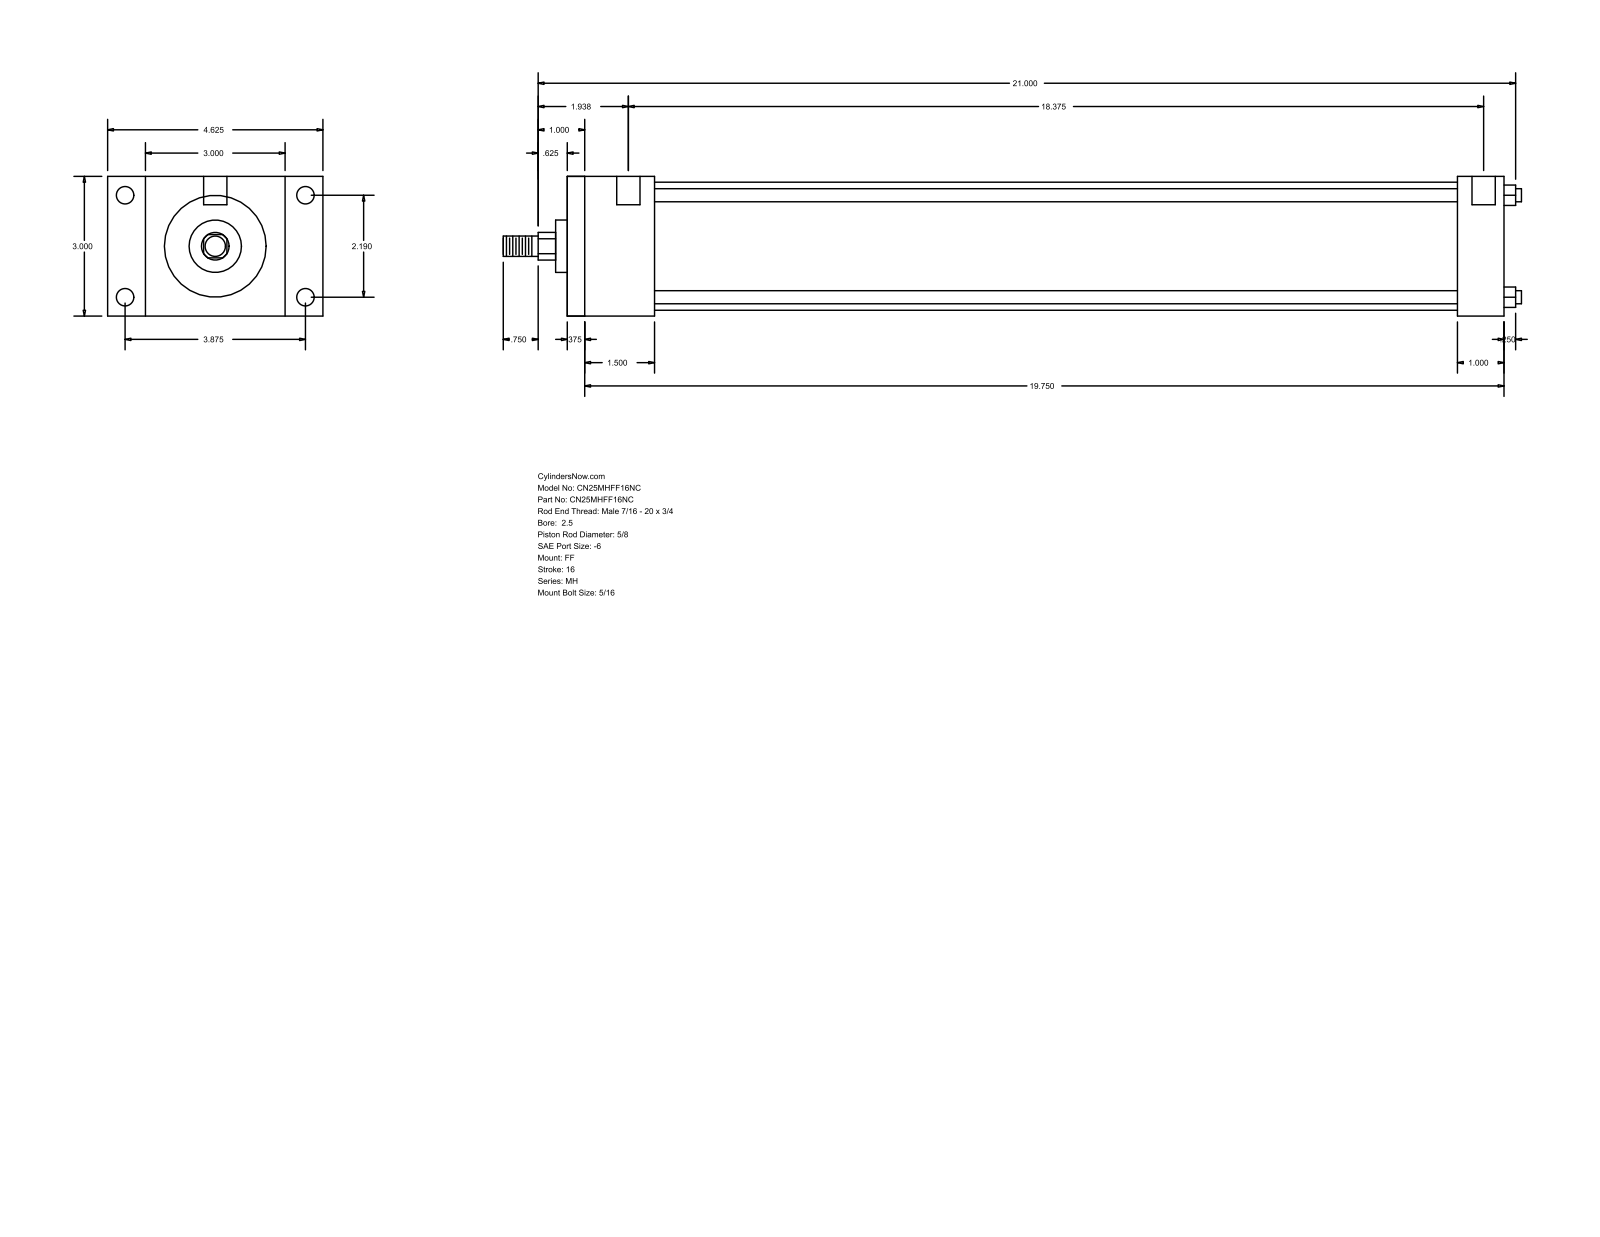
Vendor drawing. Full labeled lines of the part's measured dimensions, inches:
Part name (STEP PRODUCT): MH_FF__0250_0.625
STEP written by: GSSL Pune (CONFIG_CONTROL_DESIGN)
Units: inches
Bodies: 0 solids, 92 faces (64 planar, 28 cylindrical, 0 other)
Overall size (bounding box): 21.875 × 4.625 × 3
Round holes (diameter × count): ⌀0.219 ×4, ⌀0.375 ×4, ⌀0.5 ×2
Round bosses / shafts (diameter × count): ⌀0.281 ×4, ⌀2.75 ×1, ⌀1.125 ×1, ⌀0.625 ×1, ⌀0.437 ×1
Partial cylindrical surfaces — rounded edges, fillets, slot ends (radius × count): R0.297 ×1
Main face-to-face distances: 3, 20.125, 19.75, 0.375, 1, 1.875, 19.125, 1.5, 18.75, 17.25
Hole centre spacings: 2.19, 3.875, 4.451, 18.687, 0.125, 0.187, 18.375, 18.5
